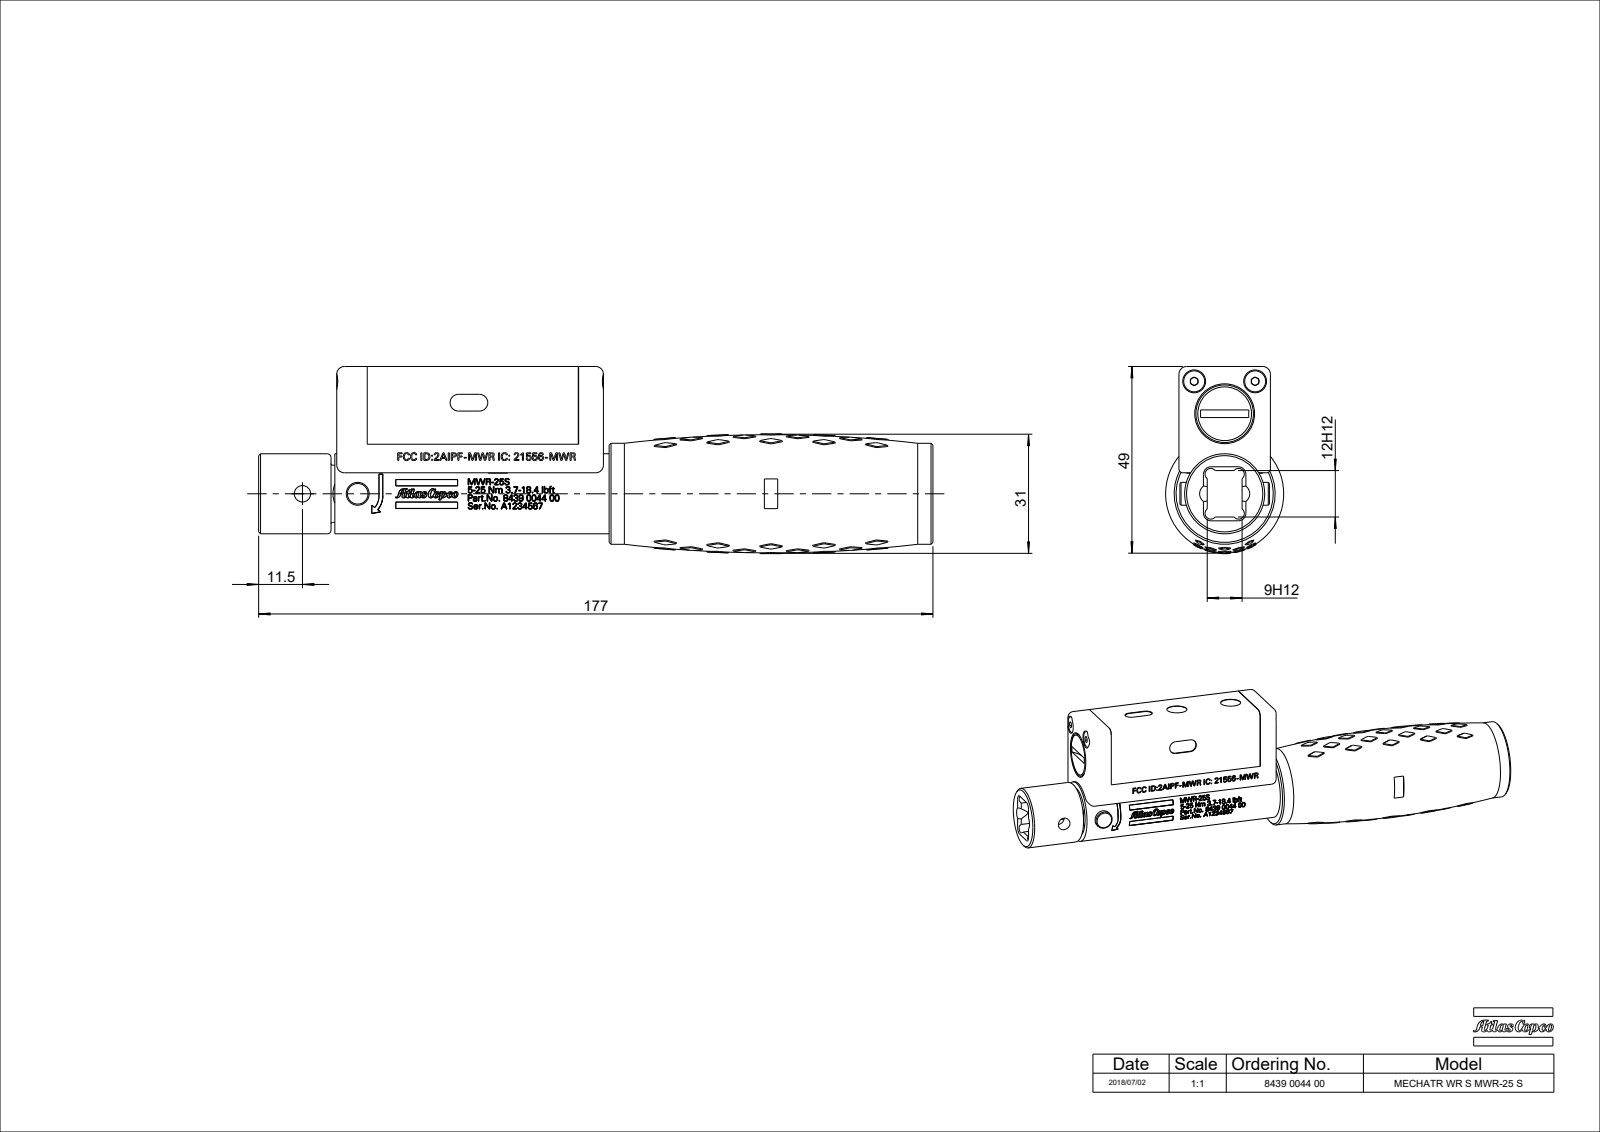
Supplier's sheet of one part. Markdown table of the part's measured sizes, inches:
| quantity | value |
| --- | --- |
| part name | 8439004400_1_SW |
| STEP written by | CREO PARAMETRIC BY PTC INC, 2016260 (CONFIG_CONTROL_DESIGN) |
| units | inches |
| bodies | 0 solids, 376 faces (21 planar, 203 cylindrical, 152 other) |
| overall size | 6.969 × 1.933 × 1.22 |
| round bosses / shafts (diameter × count) | 1.043 × 1, 0.827 × 1 |
| partial cylindrical surfaces (radius × count) | 0.079 × 9, 0.039 × 2, 0.118 × 2, 0.409 × 1 |
| main face-to-face distances | 0.945, 3.346, 3.406, 0.059, 6.161, 2.815, 2.756, 6.969, 3.622, 3.563 |
